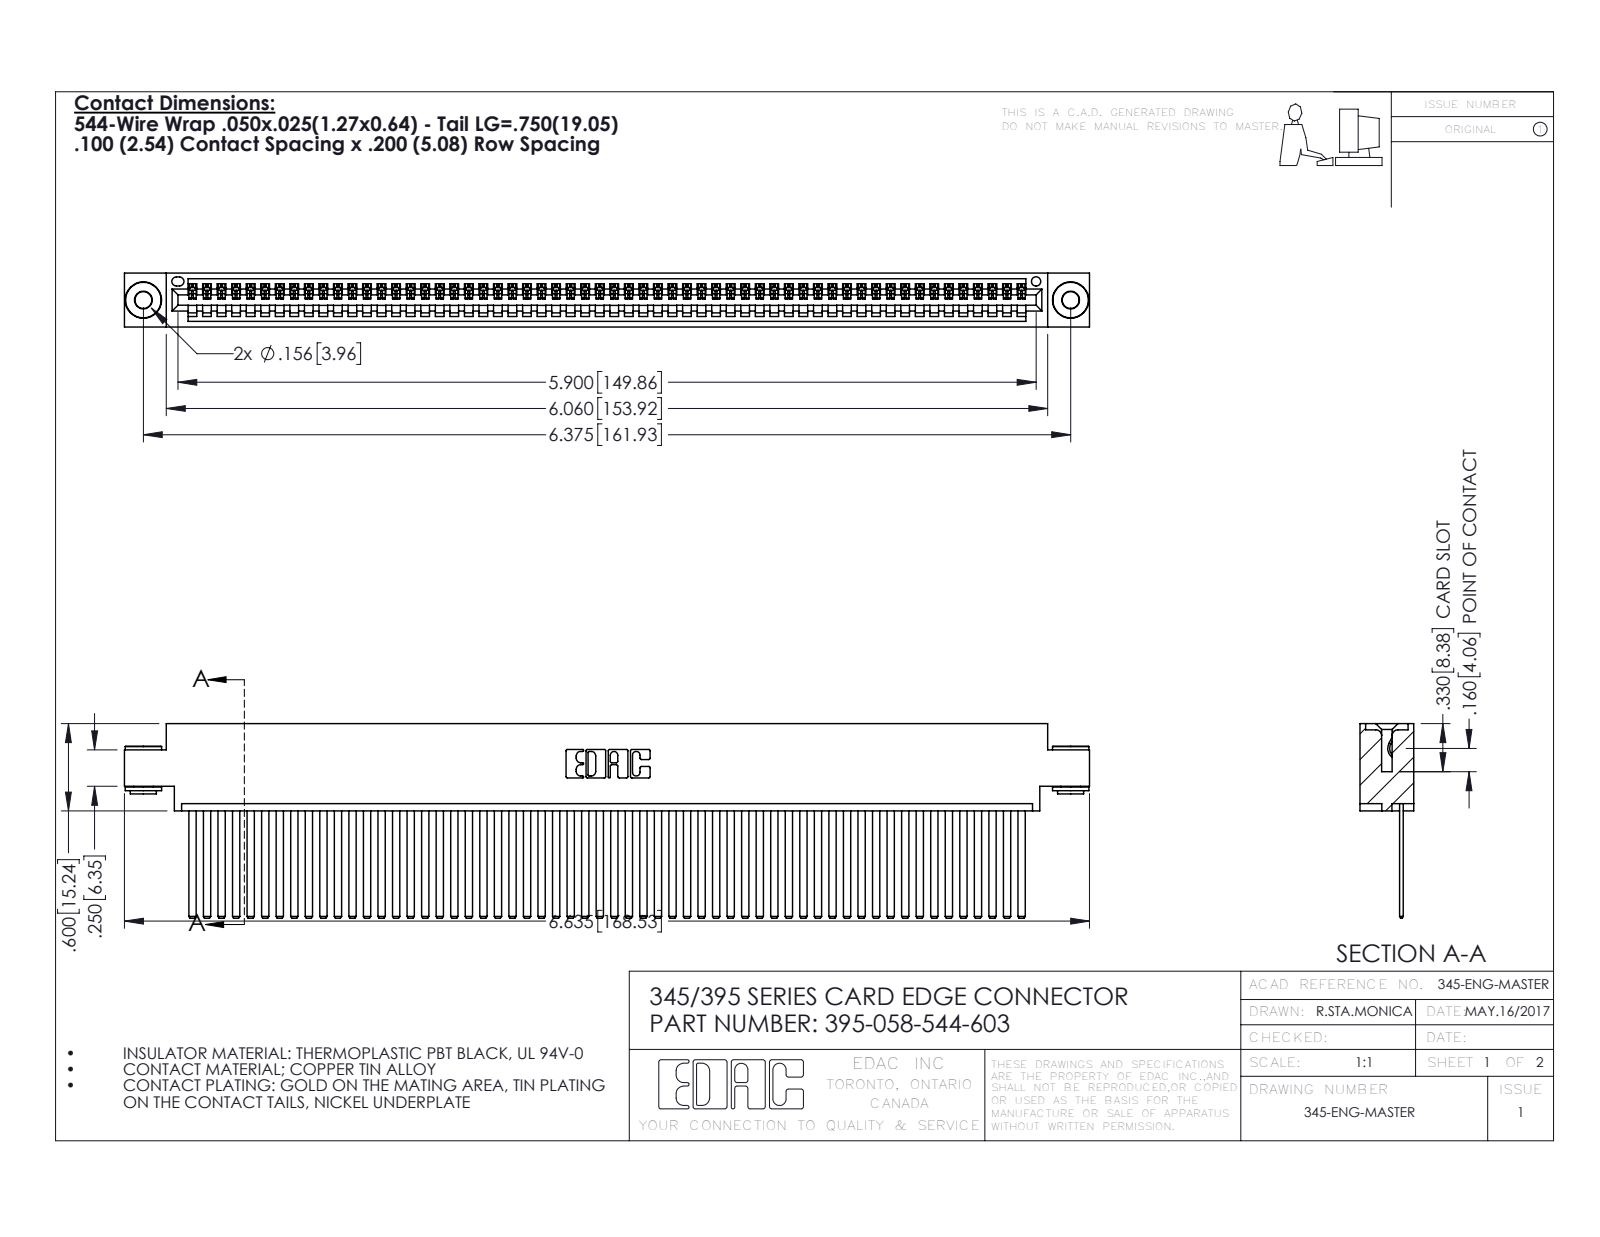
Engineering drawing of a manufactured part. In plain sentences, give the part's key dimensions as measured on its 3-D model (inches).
The part is named "345 Part_0.170 Offset - 0.156 Dia-TH; 395-058-544-603; 345-250-002_345-250-002-102; 345-292-001_345-293-144". Its 3-D file was written by "SolidWorks 2016 (CONFIG_CONTROL_DESIGN)". It is 61 solids with 3184 faces: 2182 planar, 994 cylindrical and 8 other. Overall it measures 6.635 by 1.337 by 0.37 inches. Its volume is 1.02 cubic inches and its surface area 38.42 square inches. Round holes: 2 of diameter 0.116, 2 of diameter 0.156, 1 of diameter 0.064. Round bosses or shafts: 2 of diameter 0.25, 2 of diameter 0.18, 2 of diameter 0.136. Partial cylindrical surfaces (rounded edges, fillets, slot ends): 116 of radius 0.006, 22 of radius 0.01, 6 of radius 0.007, 6 of radius 0.031, 3 of radius 0.026, 2 of radius 0.031, 2 of radius 0.04, 1 of radius 0.014. The main face-to-face distances are 0.072, 0.298, 0.025, 0.098, 0.272, 0.37, 0.2, 0.225, 0.175, 0.149. The hole center spacings are 0.27, 6.139, 6.375.
